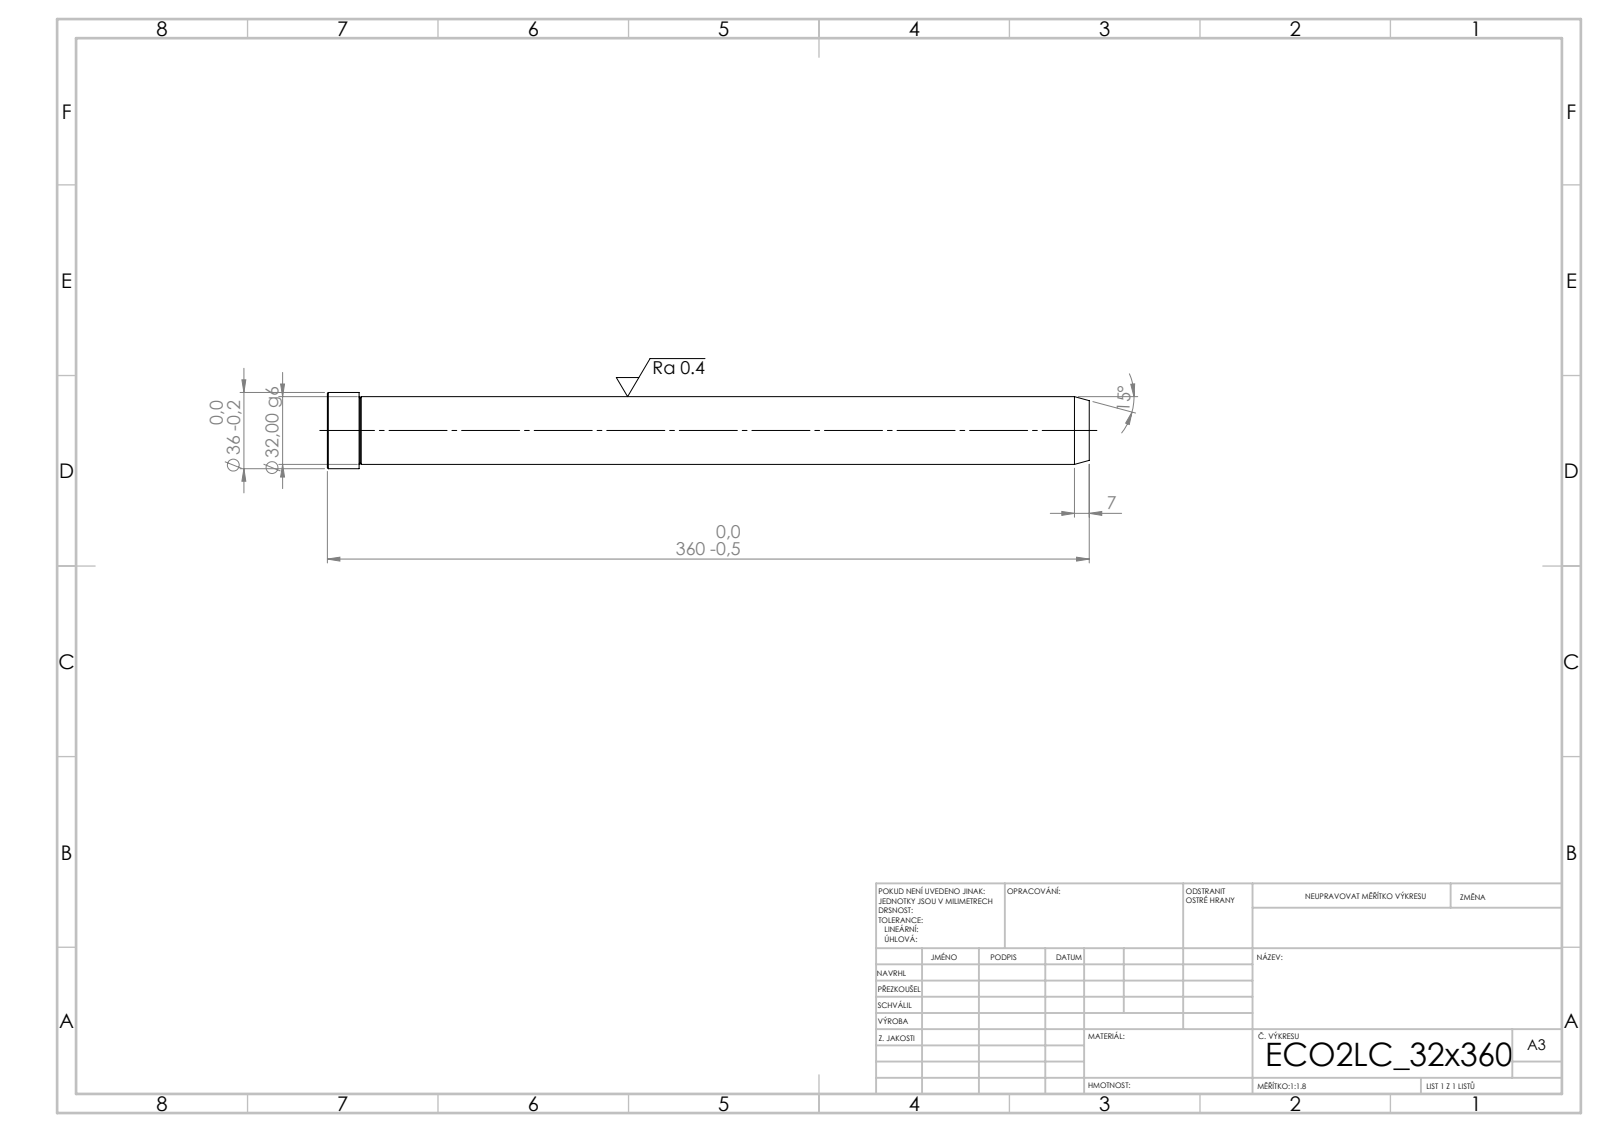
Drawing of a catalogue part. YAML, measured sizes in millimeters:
step_written_by: "SolidWorks 2019 (CONFIG_CONTROL_DESIGN)"
units: millimeters
bodies: {solids: 1, faces: 15, planar: 3, cylindrical: 4, other: 8}
overall_size: [360, 36, 36]
volume: 292046
surface_area: 38241
round_bosses_or_shafts:
  - {diameter: 36, count: 1}
  - {diameter: 32, count: 1}
face_to_face_distances: [360, 345, 15]
